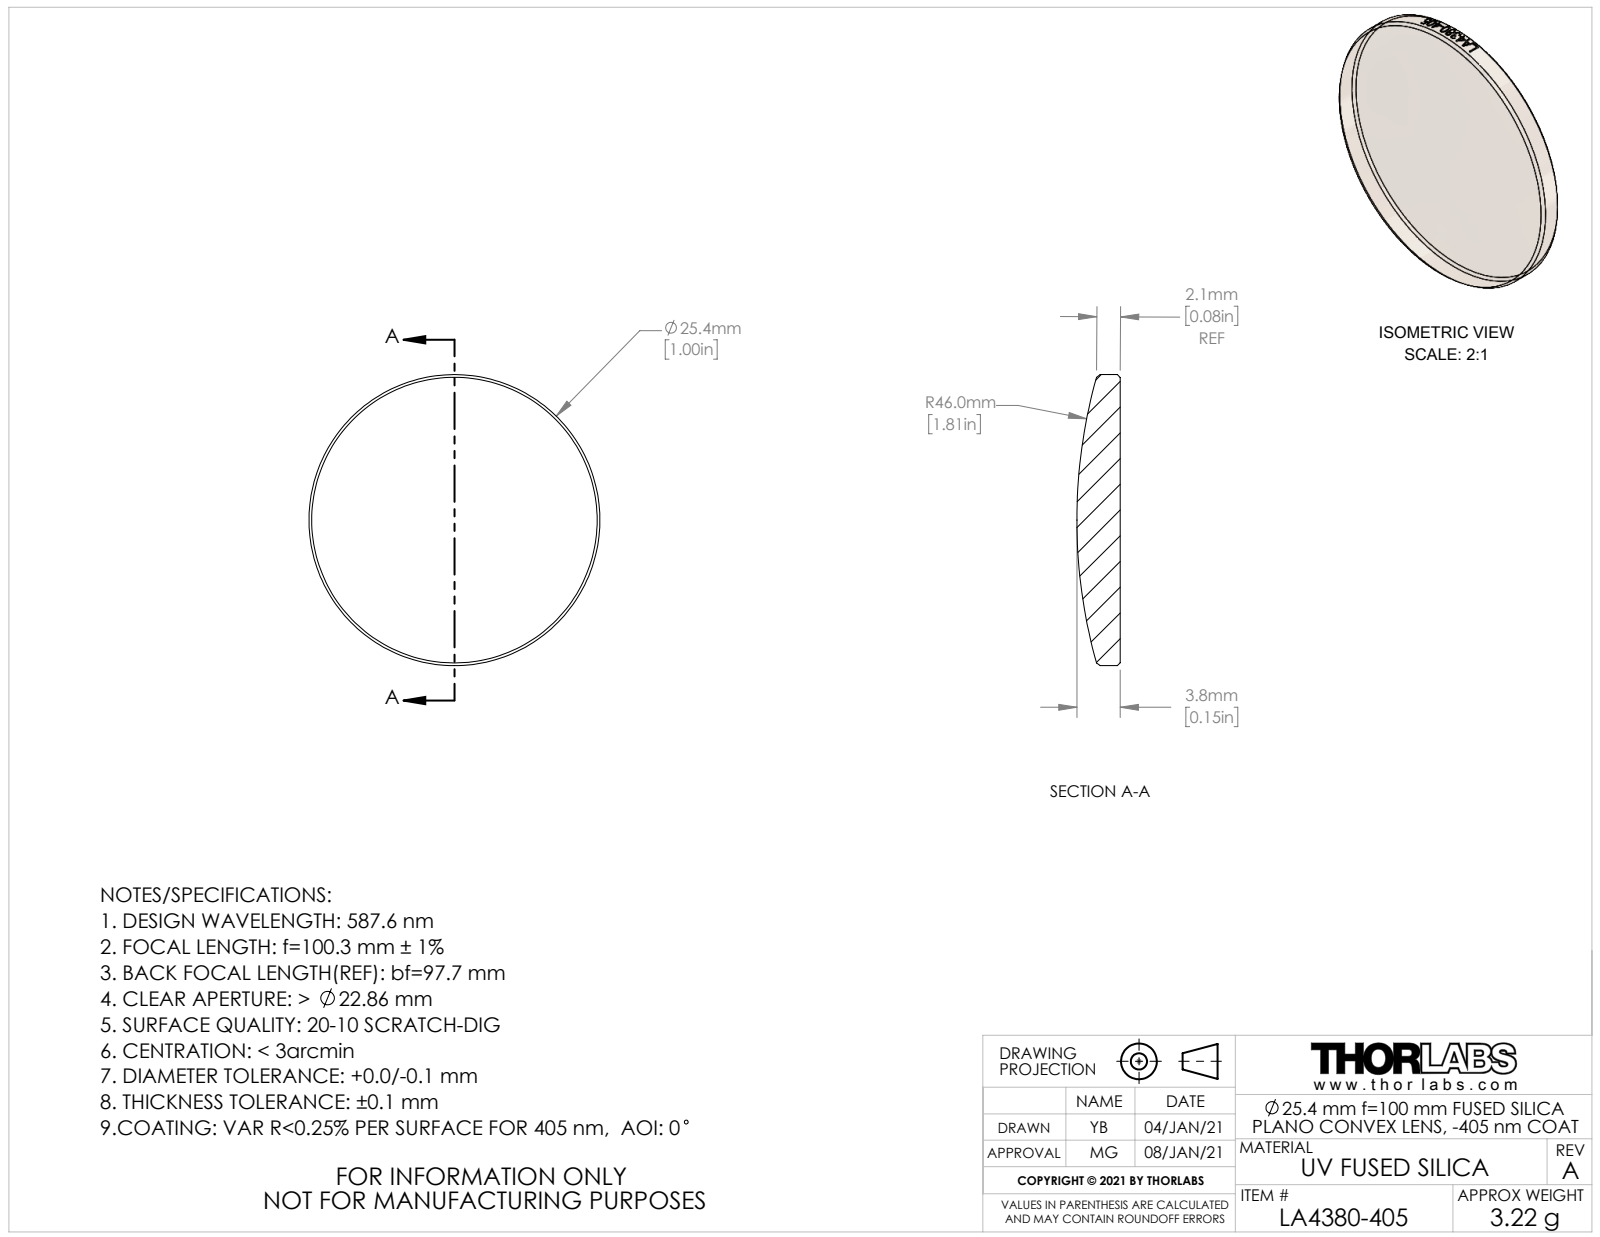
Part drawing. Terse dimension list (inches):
name: CTN016819-E0W; CTN016839
written by: SolidWorks 2018 (AUTOMOTIVE_DESIGN)
unit: in
bodies: 1 solid, 30 faces (1 planar, 23 cylindrical, 6 other)
size: 1 × 1 × 0.149
volume: 0.089 in³; area: 1.803 in²
bosses: 1× ⌀1
